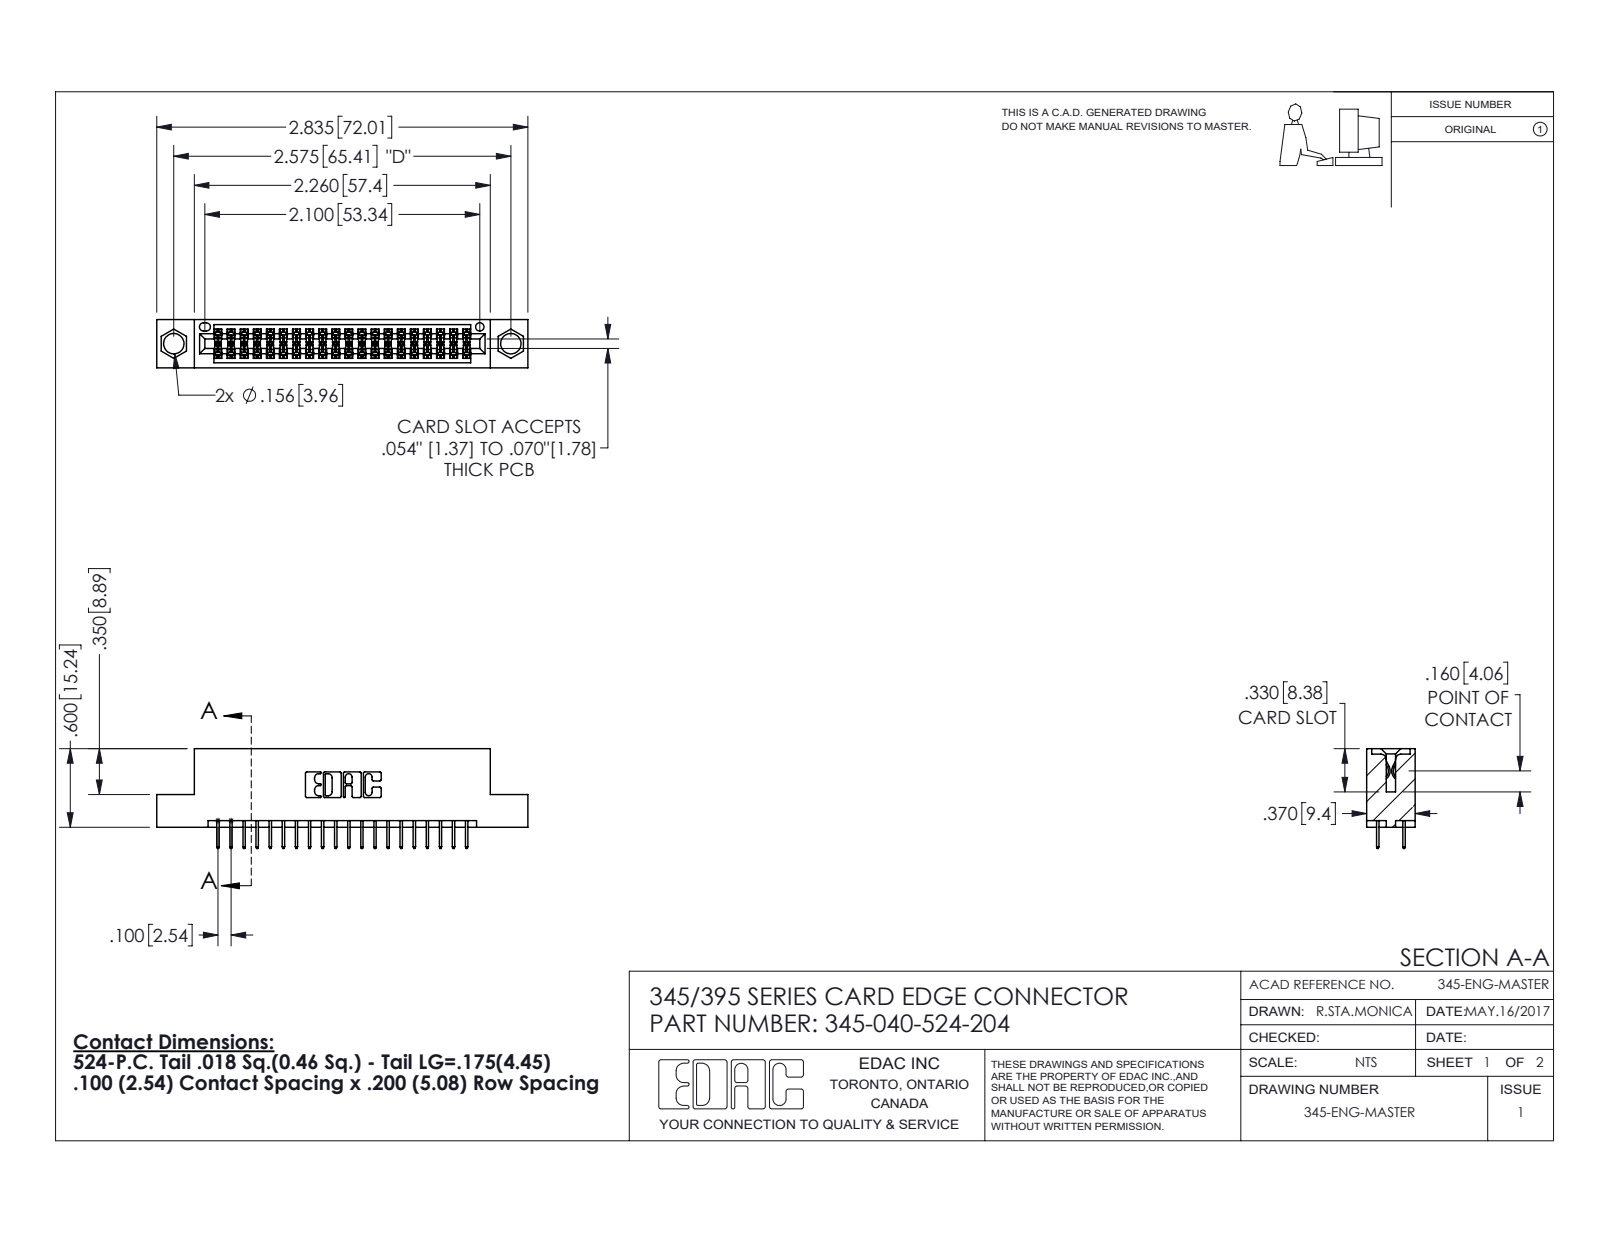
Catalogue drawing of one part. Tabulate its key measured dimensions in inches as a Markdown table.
| quantity | value |
| --- | --- |
| part name | 345-292-001_345-293-124; 345-040-524-204; 345 Part_Flush Mounting Lugs - 0.156 Dia-TI |
| STEP written by | SolidWorks 2020 (CONFIG_CONTROL_DESIGN) |
| units | inches |
| bodies | 41 solids, 2300 faces (1654 planar, 646 cylindrical, 0 other) |
| overall size | 2.835 × 0.762 × 0.37 |
| volume | 0.404 in³ |
| surface area | 14.04 in² |
| round holes (diameter × count) | 0.156 × 2, 0.064 × 1 |
| partial cylindrical surfaces (radius × count) | 0.006 × 60, 0.01 × 22, 0.007 × 6, 0.031 × 6, 0.026 × 3, 0.014 × 2, 0.019 × 2, 0.022 × 2 |
| main face-to-face distances | 0.072, 0.298, 0.2, 0.37, 0.098, 0.272, 0.025, 0.225, 0.072, 0.175 |
| hole center spacings | 0.27, 2.341, 2.575 |
